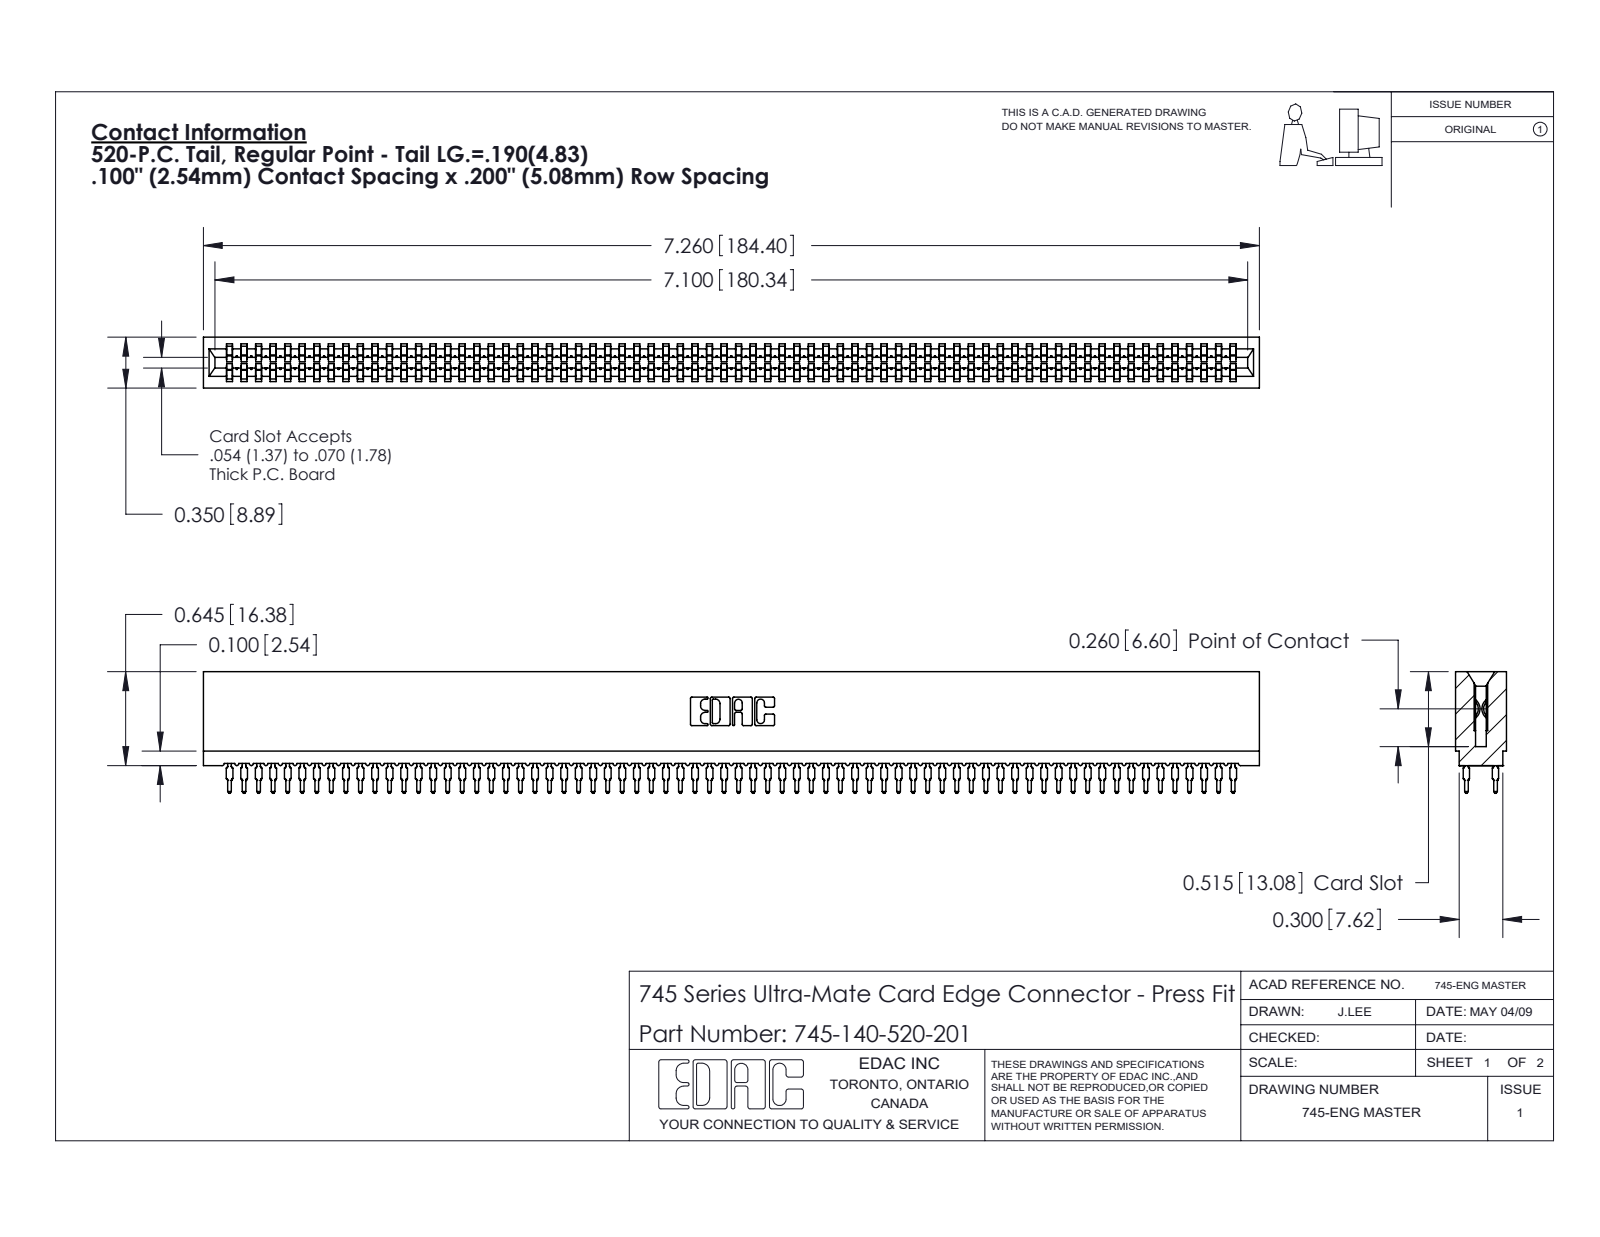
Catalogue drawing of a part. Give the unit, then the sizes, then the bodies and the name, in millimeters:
Units: millimetres
Overall size (bounding box): 184.4 × 21.2 × 8.9
Partial cylindrical surfaces — rounded edges, fillets, slot ends (radius × count): R0.5 ×280, R0.4 ×140, R0.3 ×22, R0.1 ×8, R0.3 ×8, R0.2 ×6, R0.8 ×6, R0.7 ×3
Main face-to-face distances: 8.9, 1.6, 7.3, 1.1, 7.7, 0.5, 6.2, 3.5, 5.4, 2.4
Volume: 16 300 mm³ · Surface area: 33 180 mm²
Bodies: 141 solids, 12625 faces (6495 planar, 2490 cylindrical, 3640 other)
Part name (STEP PRODUCT): 745 Part_Insulator Option - 01; 745-292-001_520; 745-140-520-201
STEP written by: SolidWorks 2020 (CONFIG_CONTROL_DESIGN)
